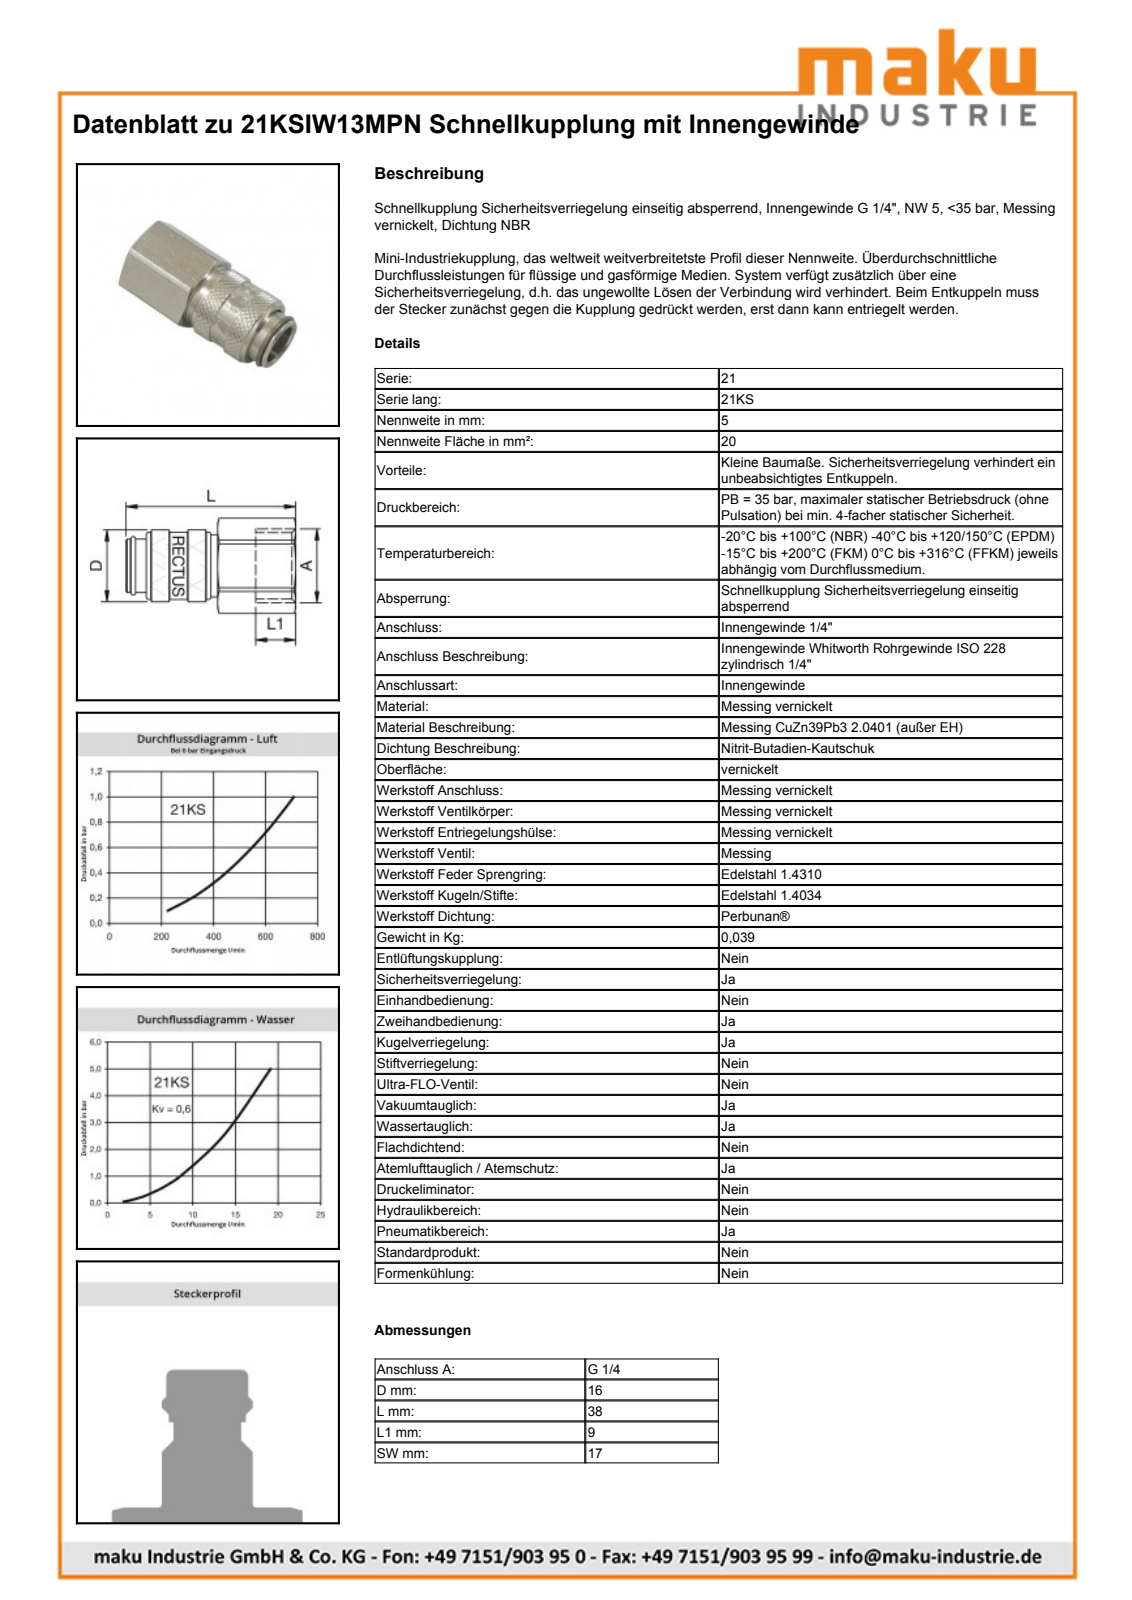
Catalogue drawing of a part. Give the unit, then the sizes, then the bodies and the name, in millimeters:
Units: millimetres
Overall size (bounding box): 38.15 × 18.72 × 18.68
Round holes (diameter × count): ⌀7.5 ×1, ⌀10.7 ×1, ⌀11.45 ×1, ⌀12.25 ×1, ⌀12.8 ×1, ⌀14 ×1
Round bosses / shafts (diameter × count): ⌀16.15 ×1, ⌀15.1 ×1, ⌀15 ×1, ⌀12 ×1, ⌀11.15 ×1, ⌀10.68 ×1
Partial cylindrical surfaces — rounded edges, fillets, slot ends (radius × count): R7.4 ×1, R9.57 ×1
Main face-to-face distances: 17, 38.15, 20.6, 17.55, 29.15, 8.55, 9, 29.14, 8.54, 9.01
Volume: 6 600 mm³ · Surface area: 4 126 mm²
Bodies: 2 solids, 418 faces (147 planar, 59 cylindrical, 212 other)
Part name (STEP PRODUCT): D105574
STEP written by: Autodesk Inventor 2011 (AUTOMOTIVE_DESIGN)
